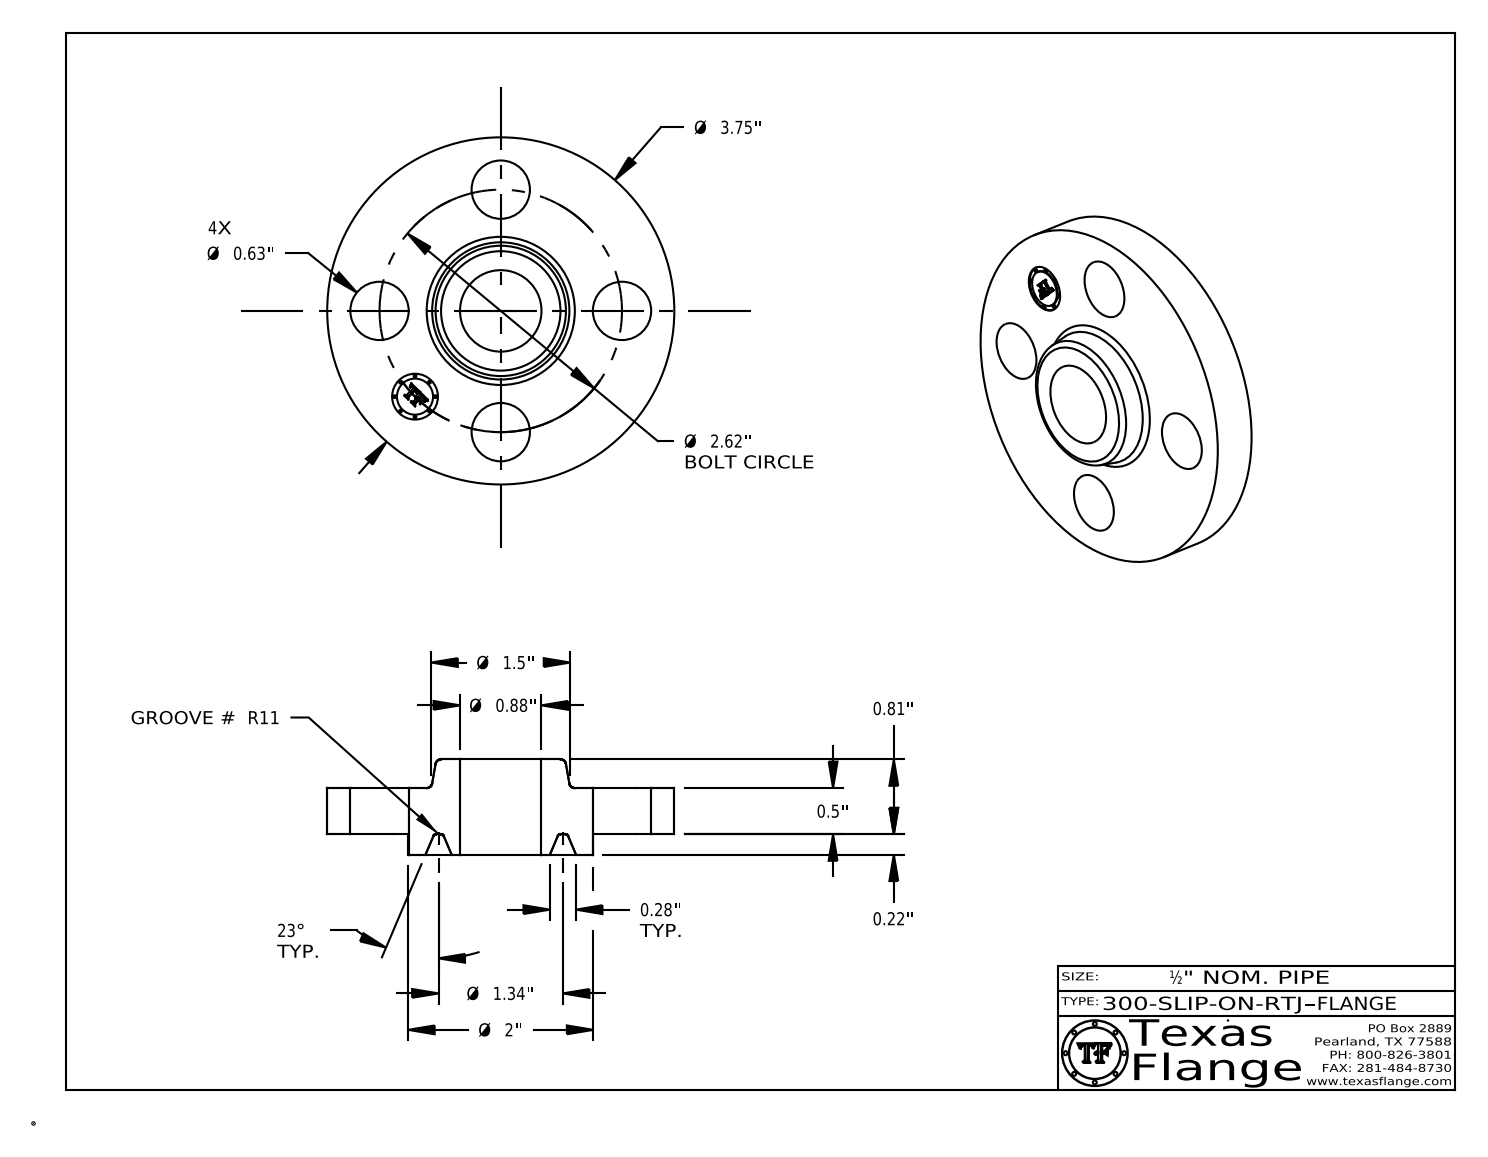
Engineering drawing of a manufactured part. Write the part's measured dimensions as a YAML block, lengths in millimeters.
part_name: "300-SLIP-ON-RTJ"
step_written_by: "CATIA V5 STEP AP214 (AUTOMOTIVE_DESIGN)"
units: millimeters
bodies: {solids: 1, faces: 423, planar: 371, cylindrical: 38, other: 14}
overall_size: [95.3, 95.3, 26.1]
volume: 86770
surface_area: 22420
round_holes:
  - {diameter: 16, count: 4}
  - {diameter: 12.6, count: 1}
  - {diameter: 22.4, count: 1}
round_bosses_or_shafts:
  - {diameter: 0.8, count: 8}
  - {diameter: 95.3, count: 1}
  - {diameter: 50.8, count: 1}
  - {diameter: 9.9, count: 1}
face_to_face_distances: [12.7, 5.6, 18.3, 26.1, 20.6, 7.9, 17.9, 12.3, 0.4, 8.3]
hole_center_spacings: [33.3, 47, 25.5, 61.5, 66.5, 33.3]
